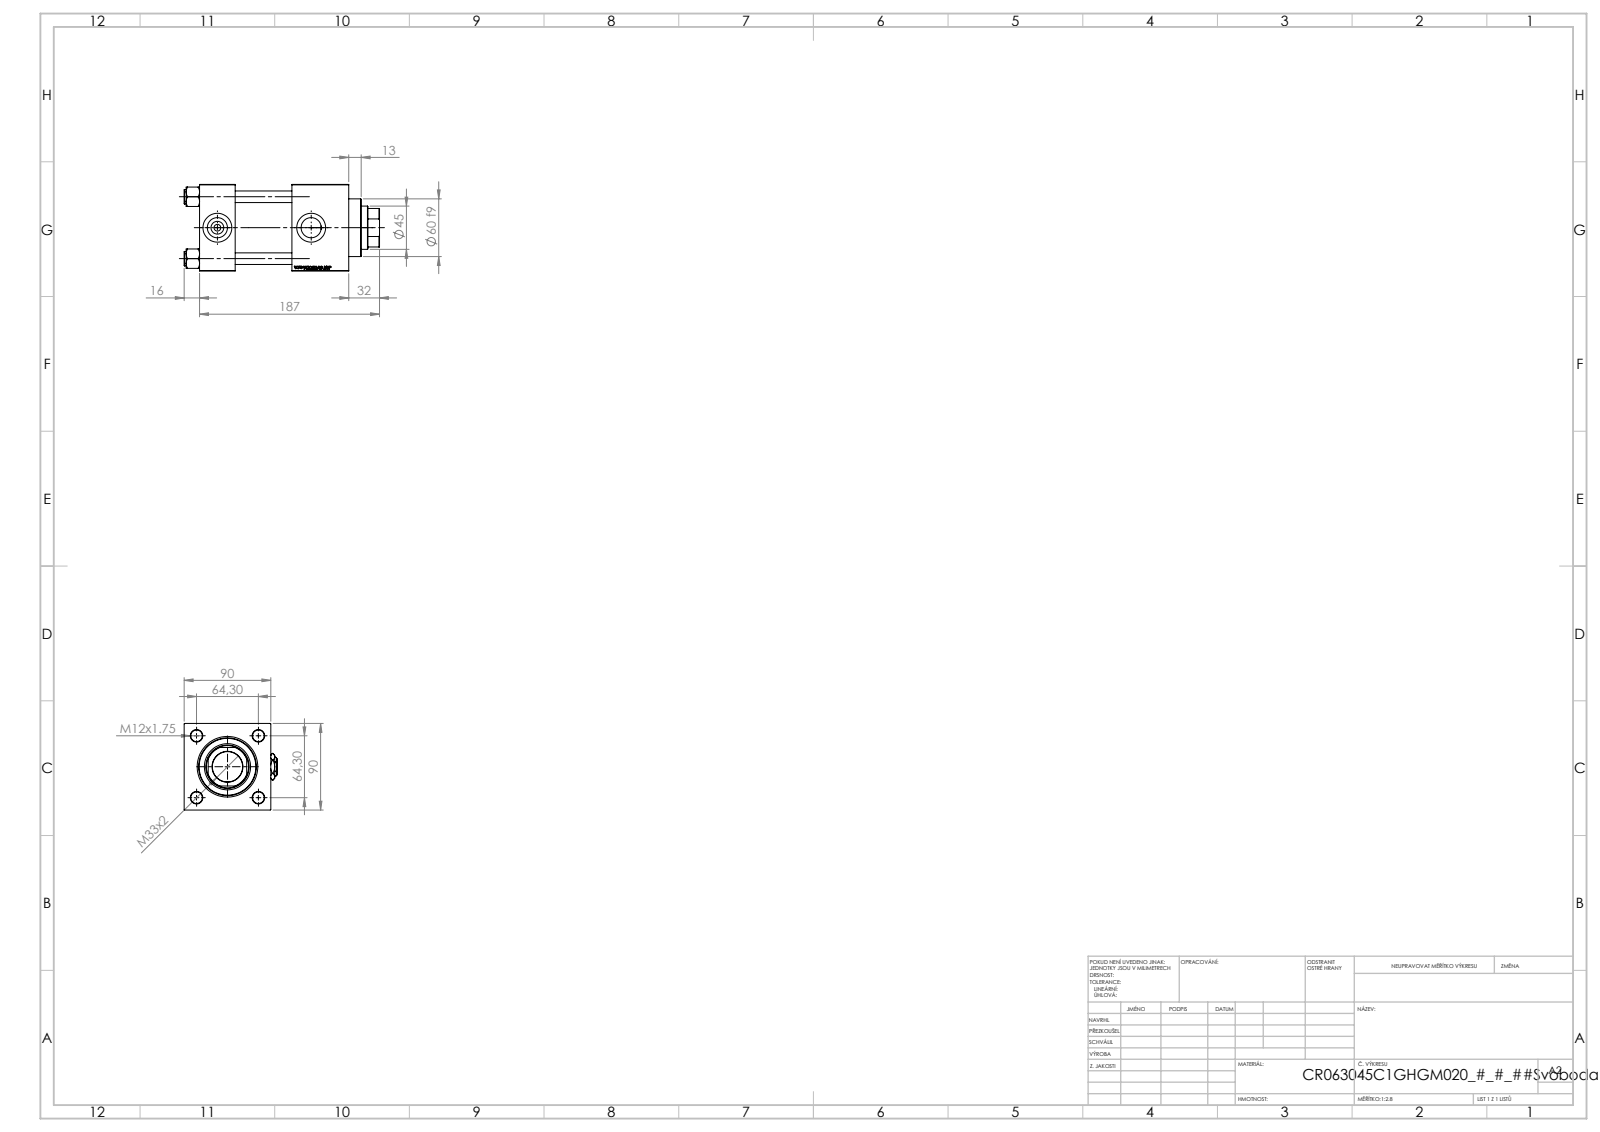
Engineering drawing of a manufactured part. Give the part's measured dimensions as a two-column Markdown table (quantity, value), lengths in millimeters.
| quantity | value |
| --- | --- |
| part name | Zatka_pro_OIL_PORT; V215CR_C_Body; V215CR_VCP_C; NUT_M5_C (+2 more) |
| STEP written by | SolidWorks 2019 (CONFIG_CONTROL_DESIGN) |
| units | millimeters |
| bodies | 12 solids, 1193 faces (549 planar, 88 cylindrical, 556 other) |
| overall size | 203 × 97 × 90 |
| volume | 993 536 mm³ |
| surface area | 192 055 mm² |
| round holes (diameter × count) | 12 × 4, 7 × 2, 20.96 × 2, 30 × 2, 31.5 × 1, 45 × 1, 48 × 1, 50 × 1, 60 × 1, 63 × 1 |
| round bosses / shafts (diameter × count) | 15 × 4, 69 × 1 |
| partial cylindrical surfaces (radius × count) | 22 × 1 |
| main face-to-face distances | 90, 59, 37, 96, 118, 155, 126.3, 89.3, 30.3, 28.7 |
| hole center spacings | 45.47, 64.3, 90.93, 97.5 |
